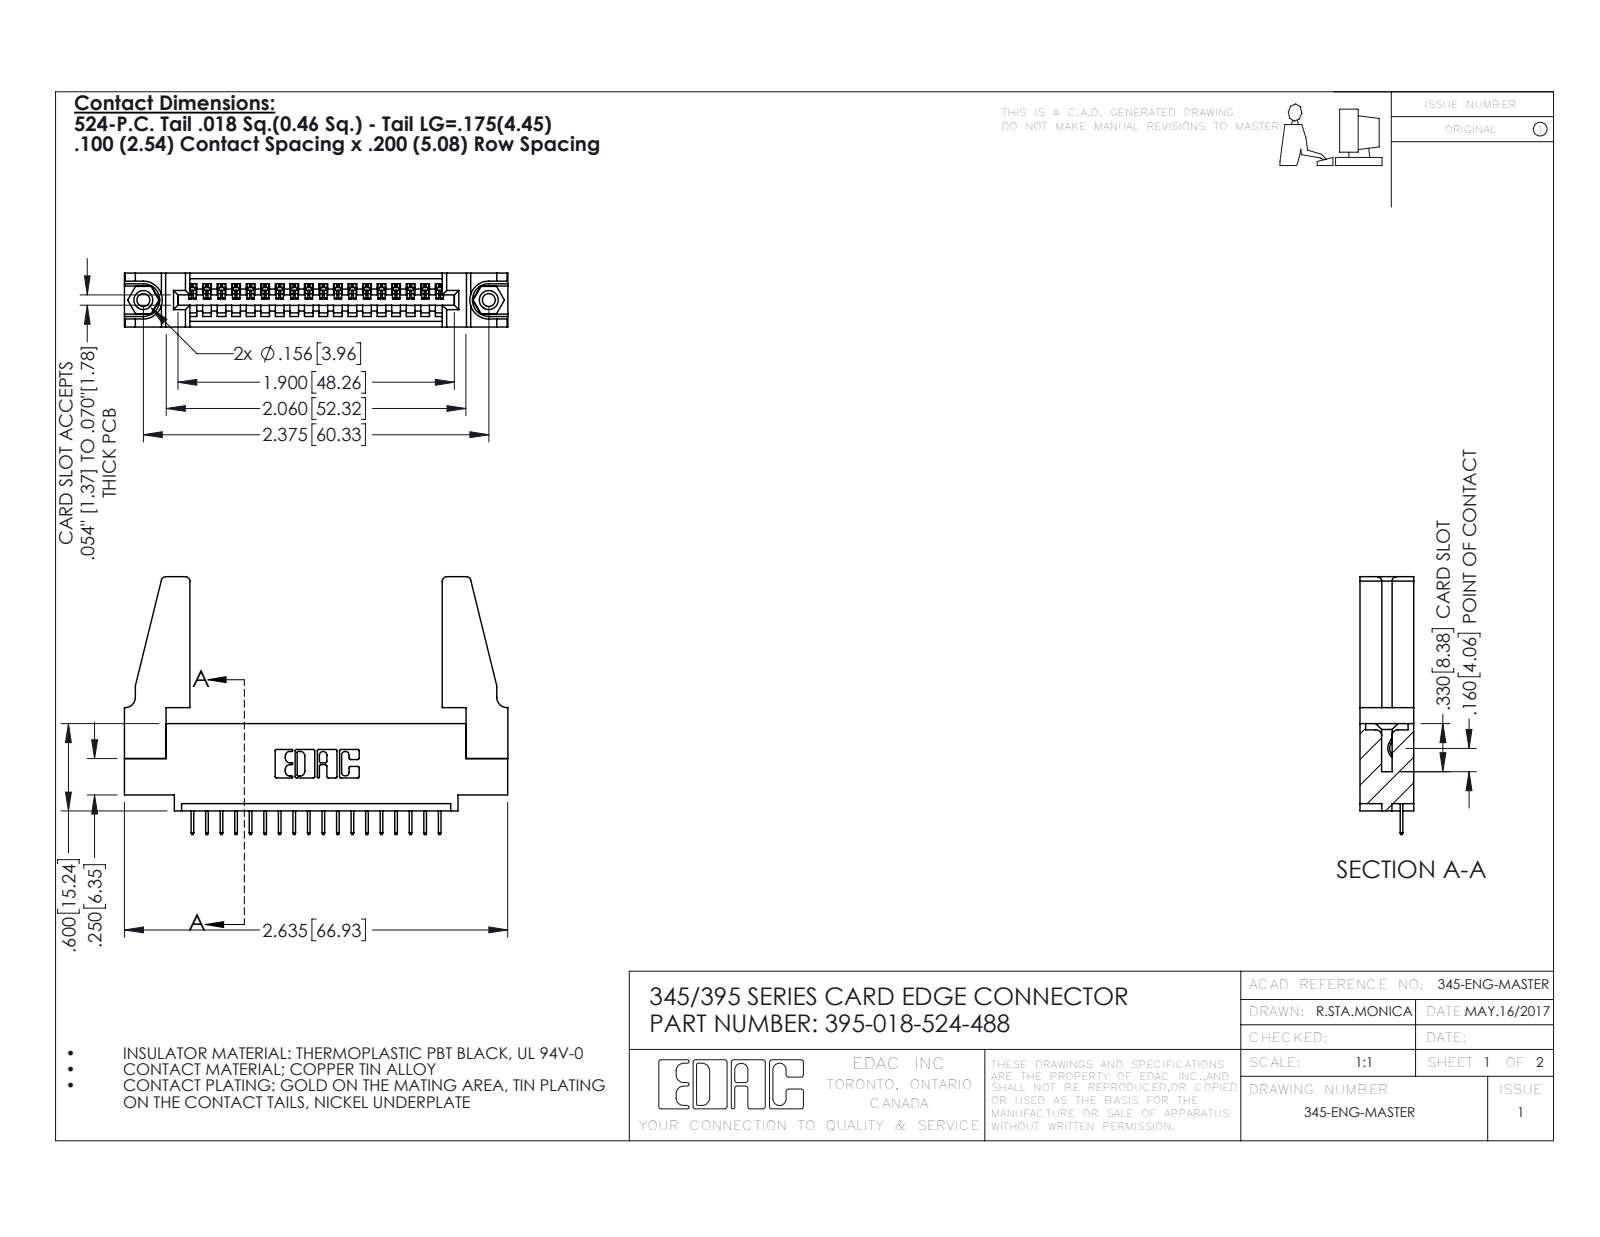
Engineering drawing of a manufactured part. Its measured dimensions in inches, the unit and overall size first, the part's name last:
Units: inches
Overall size (bounding box): 2.636 × 1.772 × 0.37
Round holes (diameter × count): ⌀0.089 ×2, ⌀0.125 ×2, ⌀0.156 ×2, ⌀0.064 ×1
Round bosses / shafts (diameter × count): ⌀0.155 ×2
Partial cylindrical surfaces — rounded edges, fillets, slot ends (radius × count): R0.006 ×36, R0.01 ×22, R0.03 ×8, R0.007 ×6, R0.031 ×6, R0.026 ×3, R0.031 ×2, R0.04 ×2
Main face-to-face distances: 0.37, 0.072, 0.298, 0.2, 0.098, 0.272, 0.025, 0.225, 0.072, 0.15
Hole centre spacings: 0.27, 2.141, 2.375
Volume: 0.566 in³ · Surface area: 16.52 in²
Bodies: 23 solids, 1370 faces (984 planar, 370 cylindrical, 16 other)
Part name (STEP PRODUCT): 395-018-524-488; 345-220-078_345-220-088; 345-292-001_345-293-124; 345-250-001_345-250-001-102 (+1 more)
STEP written by: SolidWorks 2016 (CONFIG_CONTROL_DESIGN)
